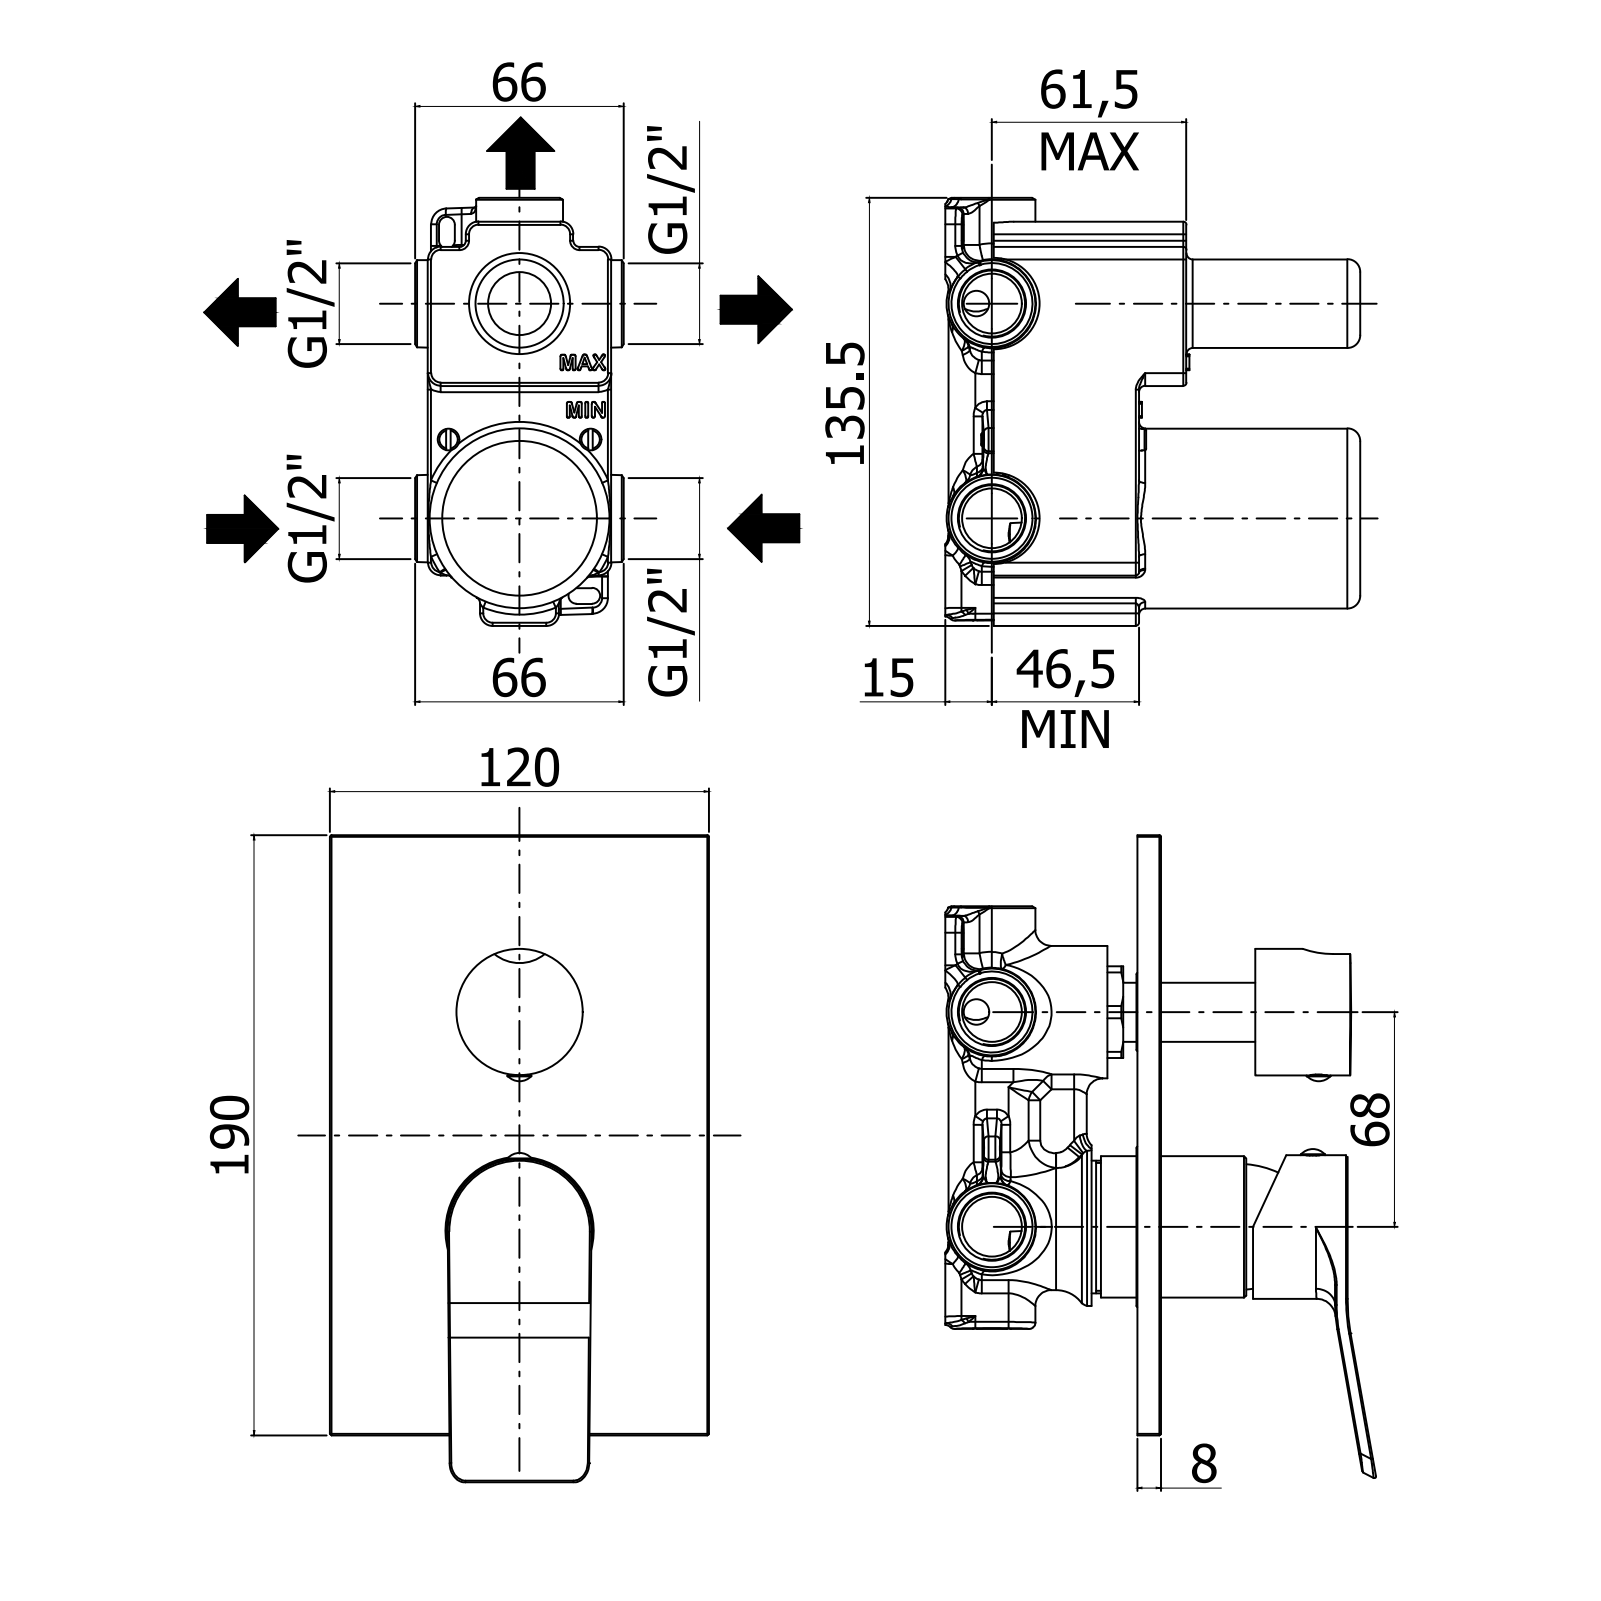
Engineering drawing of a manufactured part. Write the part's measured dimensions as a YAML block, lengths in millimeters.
part_name: "TI019CR"
step_written_by: "CREO PARAMETRIC BY PTC INC, 2020044 (CONFIG_CONTROL_DESIGN)"
units: millimeters
bodies: {solids: 2, faces: 231, planar: 72, cylindrical: 93, other: 66}
overall_size: [203.58, 120, 64.05]
volume: 246676
surface_area: 87114
round_holes:
  - {diameter: 3, count: 2}
  - {diameter: 4.2, count: 2}
  - {diameter: 36, count: 2}
  - {diameter: 3.2, count: 1}
  - {diameter: 11, count: 1}
  - {diameter: 14.8, count: 1}
  - {diameter: 30.6, count: 1}
  - {diameter: 37.5, count: 1}
round_bosses_or_shafts:
  - {diameter: 7.6, count: 2}
  - {diameter: 5.5, count: 2}
  - {diameter: 45.5, count: 1}
  - {diameter: 44.8, count: 1}
  - {diameter: 40, count: 1}
  - {diameter: 24, count: 1}
  - {diameter: 18.7, count: 1}
partial_cylinders:
  - {radius: 0.5, count: 18}
  - {radius: 1.5, count: 2}
  - {radius: 5, count: 2}
  - {radius: 12.5, count: 1}
  - {radius: 44.14, count: 1}
  - {radius: 63, count: 1}
face_to_face_distances: [8, 4.02, 55.1, 47.1, 120, 4, 51.1, 43.1, 25.2, 17.9]
hole_center_spacings: [1.8, 10, 68, 78]
